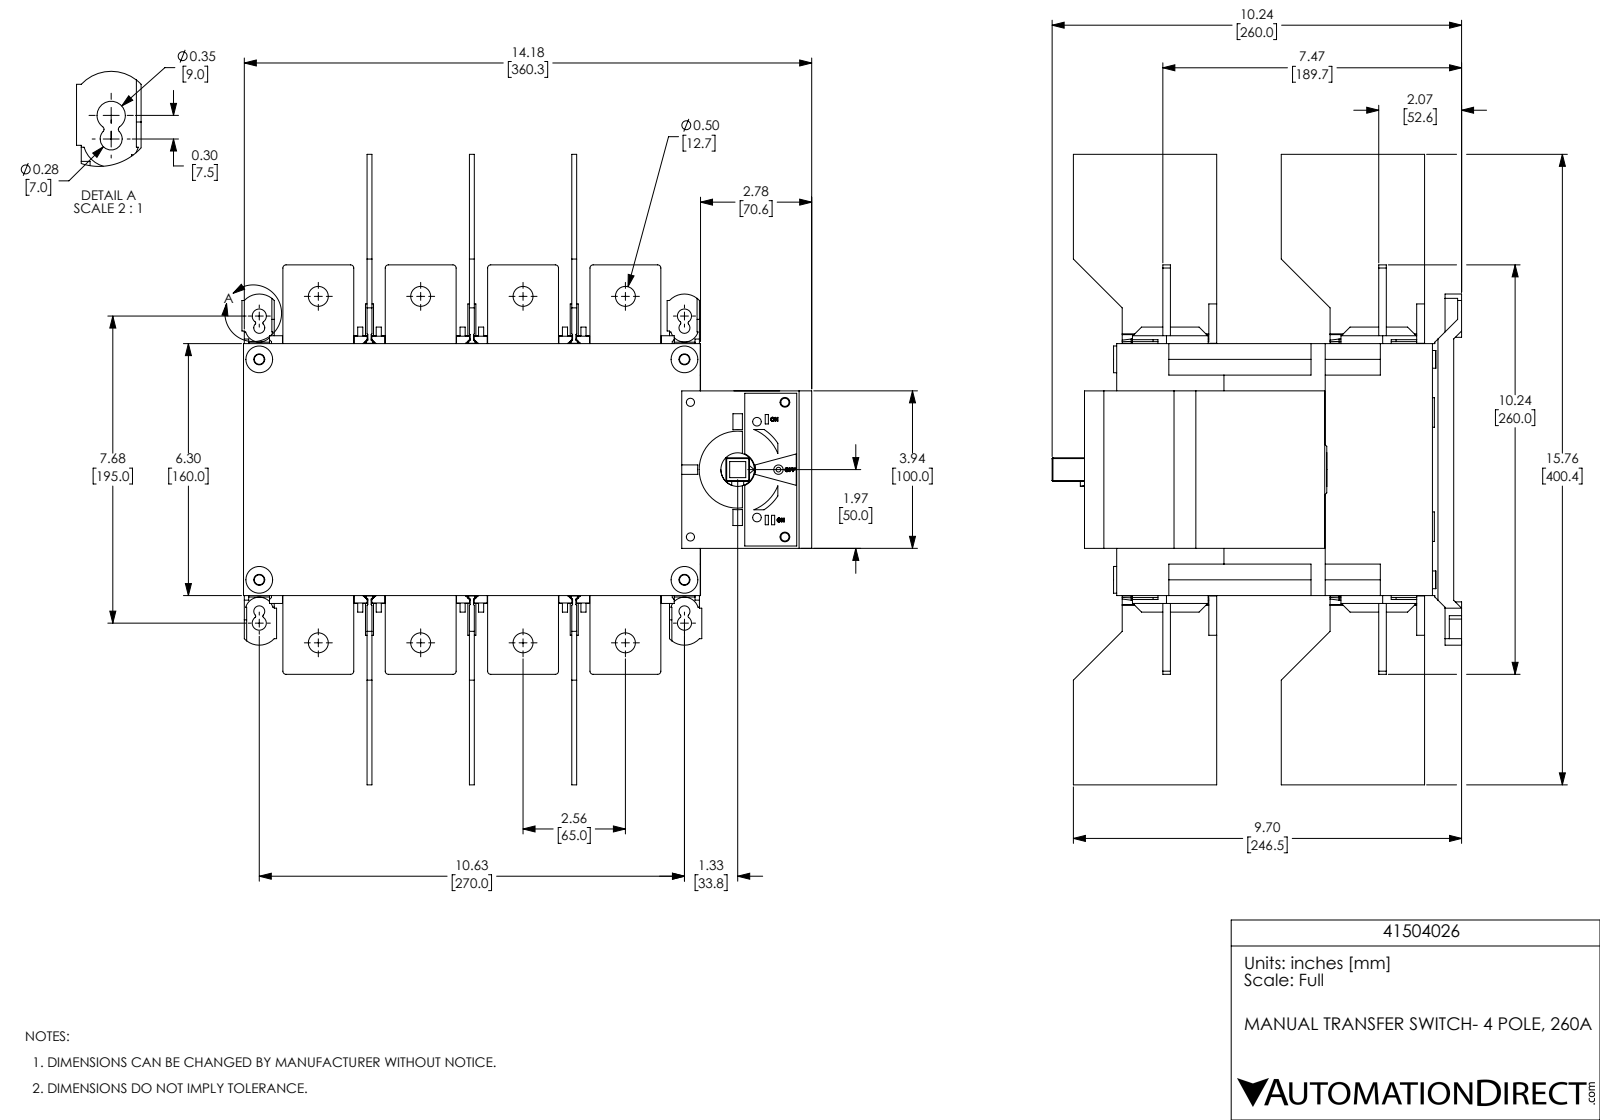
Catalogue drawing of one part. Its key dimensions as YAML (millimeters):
part_name: "41504026"
step_written_by: "SolidWorks 2017 (AUTOMOTIVE_DESIGN)"
units: millimeters
bodies: {solids: 15, faces: 1717, planar: 1427, cylindrical: 284, other: 6}
overall_size: [400.4, 361.8, 260]
volume: 10160000
surface_area: 808400
round_holes:
  - {diameter: 6.3, count: 12}
  - {diameter: 12.7, count: 8}
  - {diameter: 5.2, count: 4}
  - {diameter: 7, count: 4}
  - {diameter: 9, count: 4}
  - {diameter: 12, count: 4}
  - {diameter: 5.5, count: 2}
  - {diameter: 3, count: 1}
  - {diameter: 21.5, count: 1}
round_bosses_or_shafts:
  - {diameter: 17, count: 4}
  - {diameter: 21.4, count: 1}
  - {diameter: 6, count: 1}
partial_cylinders:
  - {radius: 2, count: 16}
  - {radius: 8.7, count: 12}
  - {radius: 1, count: 8}
  - {radius: 5.5, count: 8}
  - {radius: 1.2, count: 4}
  - {radius: 3.5, count: 4}
  - {radius: 6, count: 4}
  - {radius: 9, count: 4}
face_to_face_distances: [65, 3.1, 130, 68.1, 61.9, 160, 78.5, 81.6, 143.5, 146.6]
hole_center_spacings: [65, 130, 229.4, 270, 277.7, 27.5, 37.5, 39.5]
